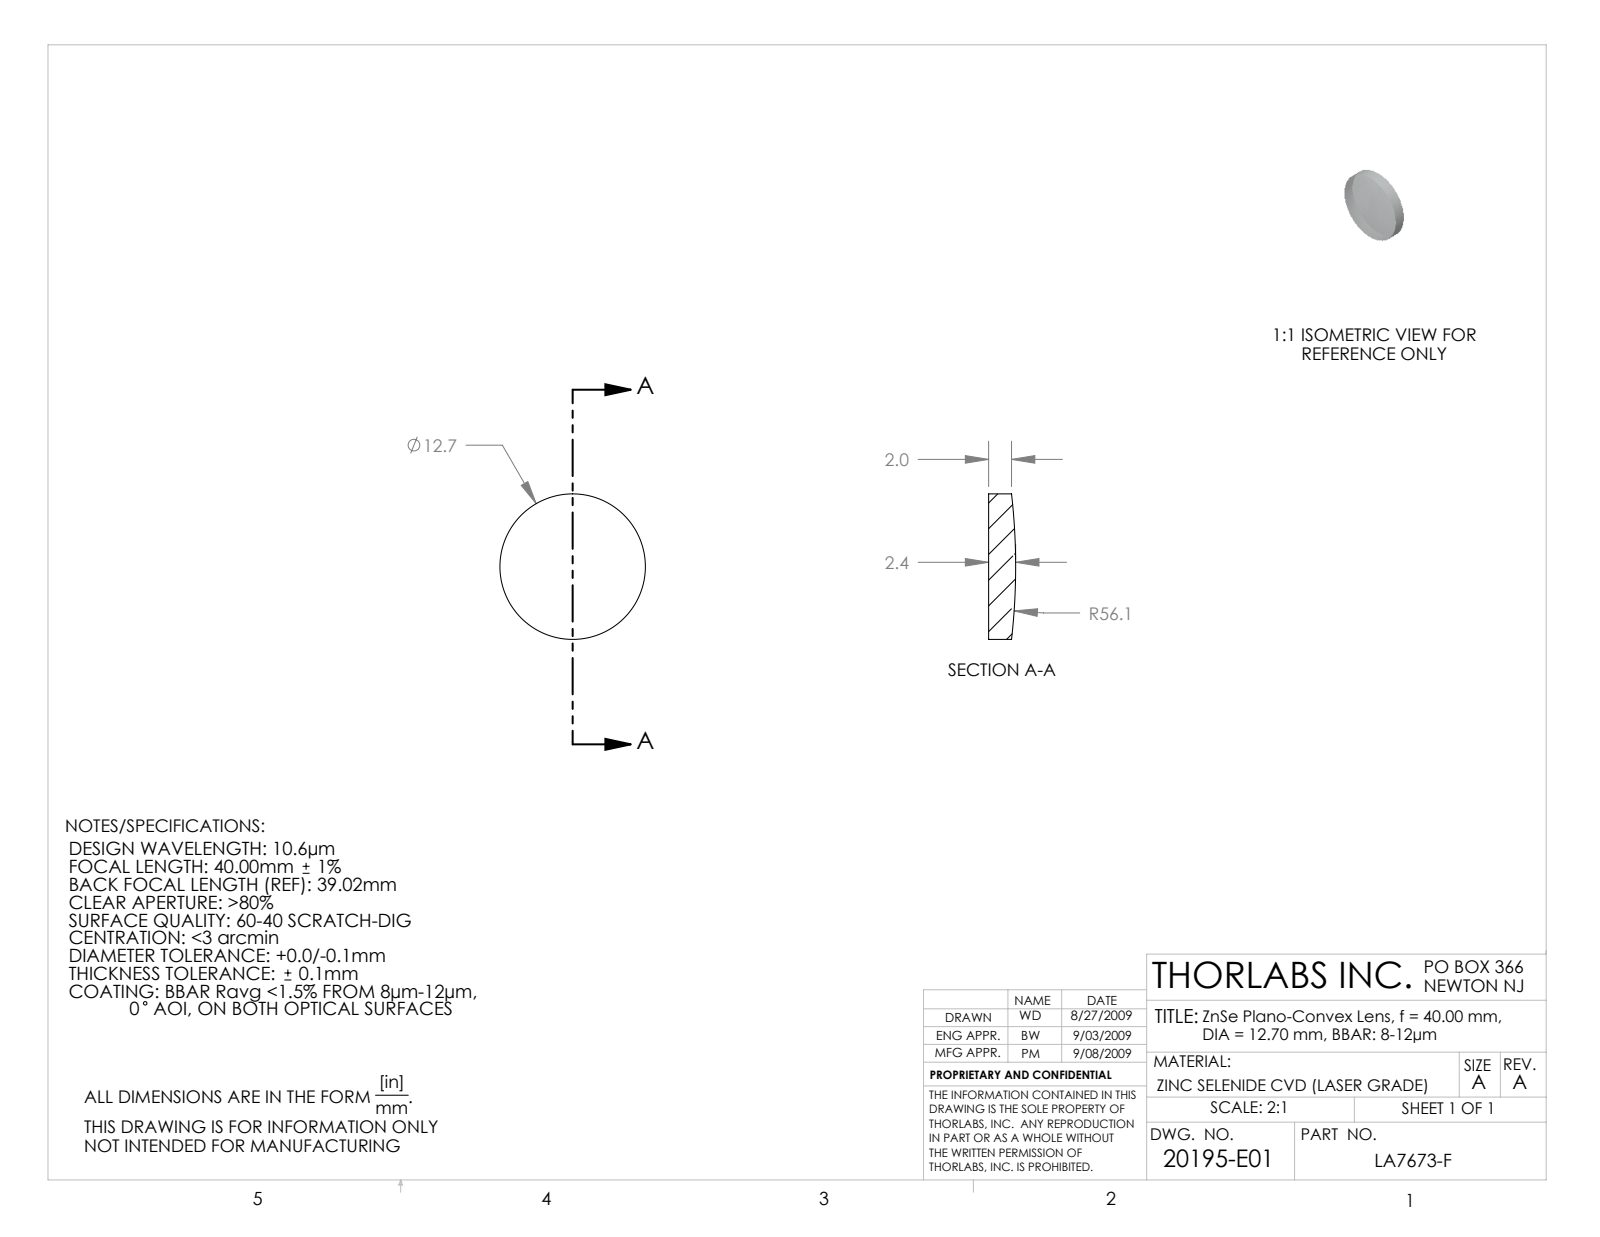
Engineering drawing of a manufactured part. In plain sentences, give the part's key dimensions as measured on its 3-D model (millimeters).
The part is named "20195-E0W". Its 3-D file was written by "SolidWorks 2007 (CONFIG_CONTROL_DESIGN)". It is 1 solid with 5 faces: 1 planar, 2 cylindrical and 2 other. Overall it measures 12.7 by 12.7 by 2.36 millimeters. Its volume is 276 cubic millimeters and its surface area 334 square millimeters. Round bosses or shafts: 1 of diameter 12.7.
